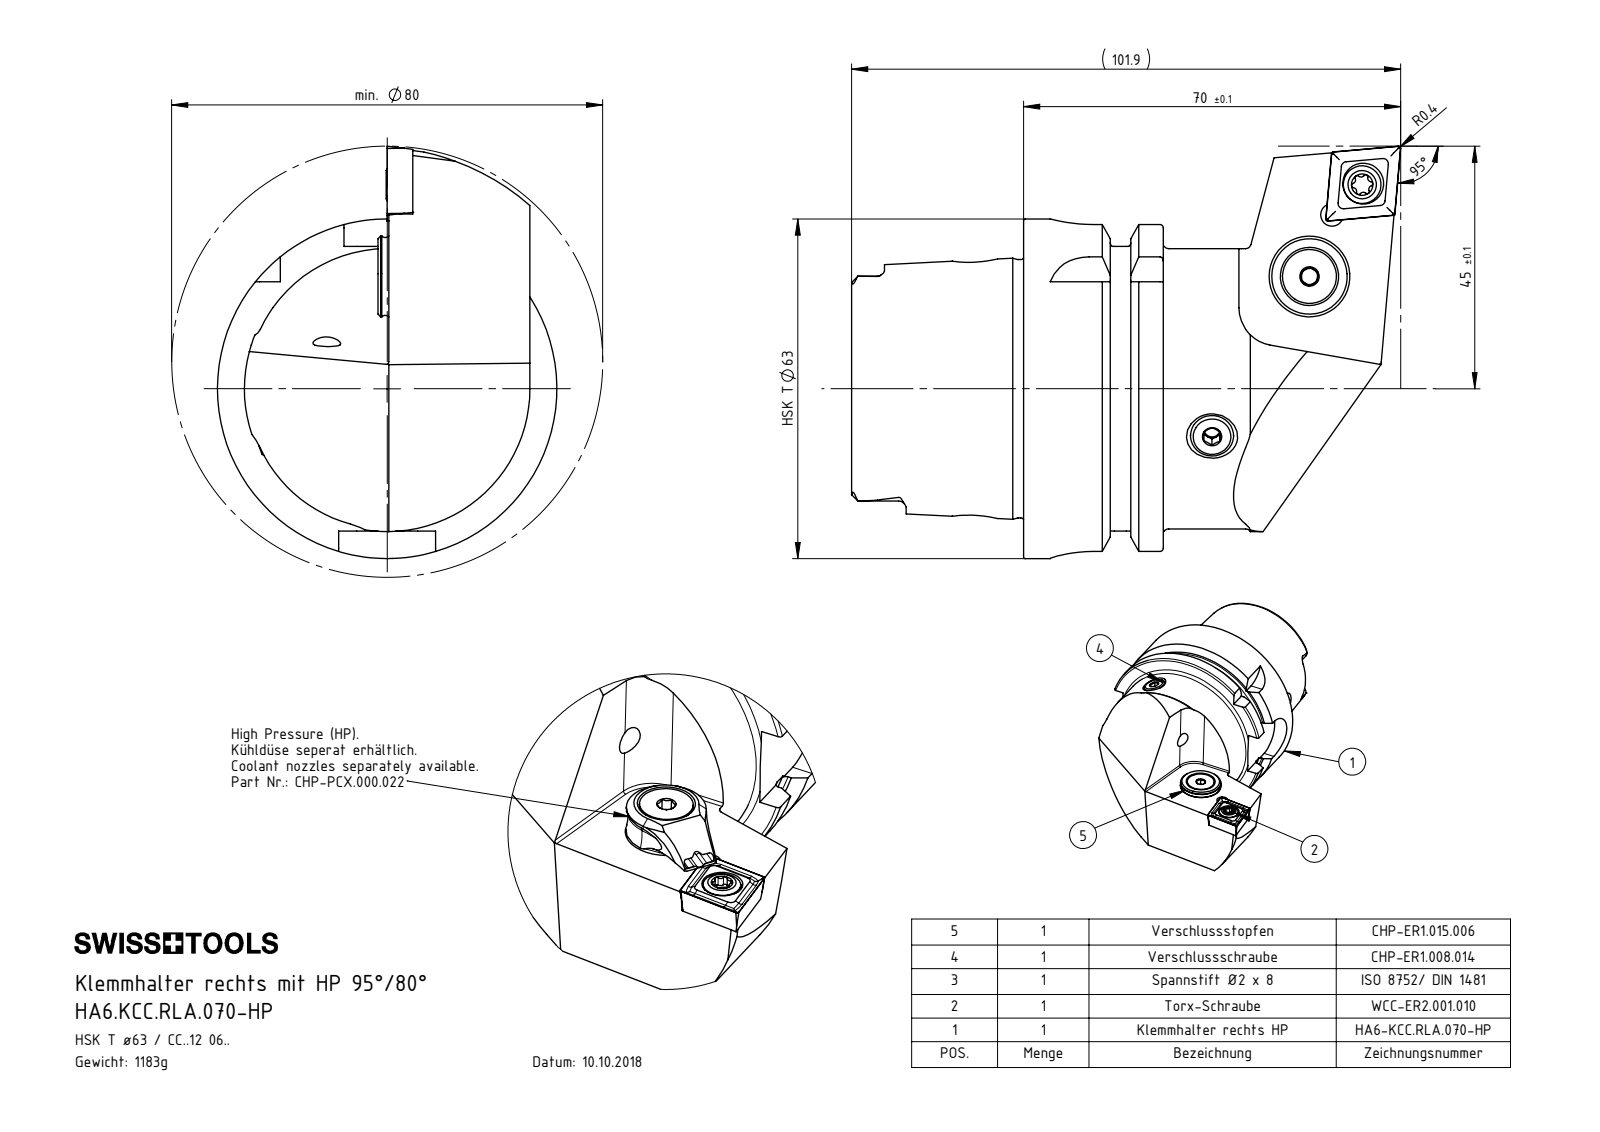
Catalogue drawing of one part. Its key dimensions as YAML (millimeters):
part_name: "HA6-KCC.RLA.070-HP_B; HA6.KCC.RLA.070-HP; DIN 3771 - 13x1; CHP-ER1.015.006 (+6 more)"
step_written_by: "SolidWorks 2017 (AUTOMOTIVE_DESIGN)"
units: millimeters
bodies: {solids: 8, faces: 301, planar: 116, cylindrical: 75, other: 110}
overall_size: [101.9, 76.5, 63]
volume: 150671
surface_area: 33879
round_holes:
  - {diameter: 4.2, count: 4}
  - {diameter: 5, count: 2}
  - {diameter: 1.2, count: 1}
  - {diameter: 2, count: 1}
  - {diameter: 2.5, count: 1}
  - {diameter: 3, count: 1}
  - {diameter: 5.2, count: 1}
  - {diameter: 5.5, count: 1}
  - {diameter: 7, count: 1}
  - {diameter: 7.5, count: 1}
  - {diameter: 7.6, count: 1}
  - {diameter: 8.4, count: 1}
round_bosses_or_shafts:
  - {diameter: 5, count: 2}
  - {diameter: 63, count: 1}
  - {diameter: 54.95, count: 1}
  - {diameter: 52, count: 1}
  - {diameter: 47.94, count: 1}
  - {diameter: 15, count: 1}
  - {diameter: 13.4, count: 1}
  - {diameter: 10, count: 1}
partial_cylinders:
  - {radius: 0.39, count: 6}
  - {radius: 1.4, count: 6}
  - {radius: 8, count: 4}
  - {radius: 0.69, count: 3}
  - {radius: 0.69, count: 3}
  - {radius: 0.5, count: 2}
  - {radius: 2.82, count: 2}
  - {radius: 2.88, count: 2}
face_to_face_distances: [26.2, 25.95, 16, 9.95, 31.9, 41.85, 57.85, 52.8, 21.8, 11.85]
hole_center_spacings: [4.49, 7.93, 8.2, 8.25, 12.15, 16.1, 16.36, 19.63]
